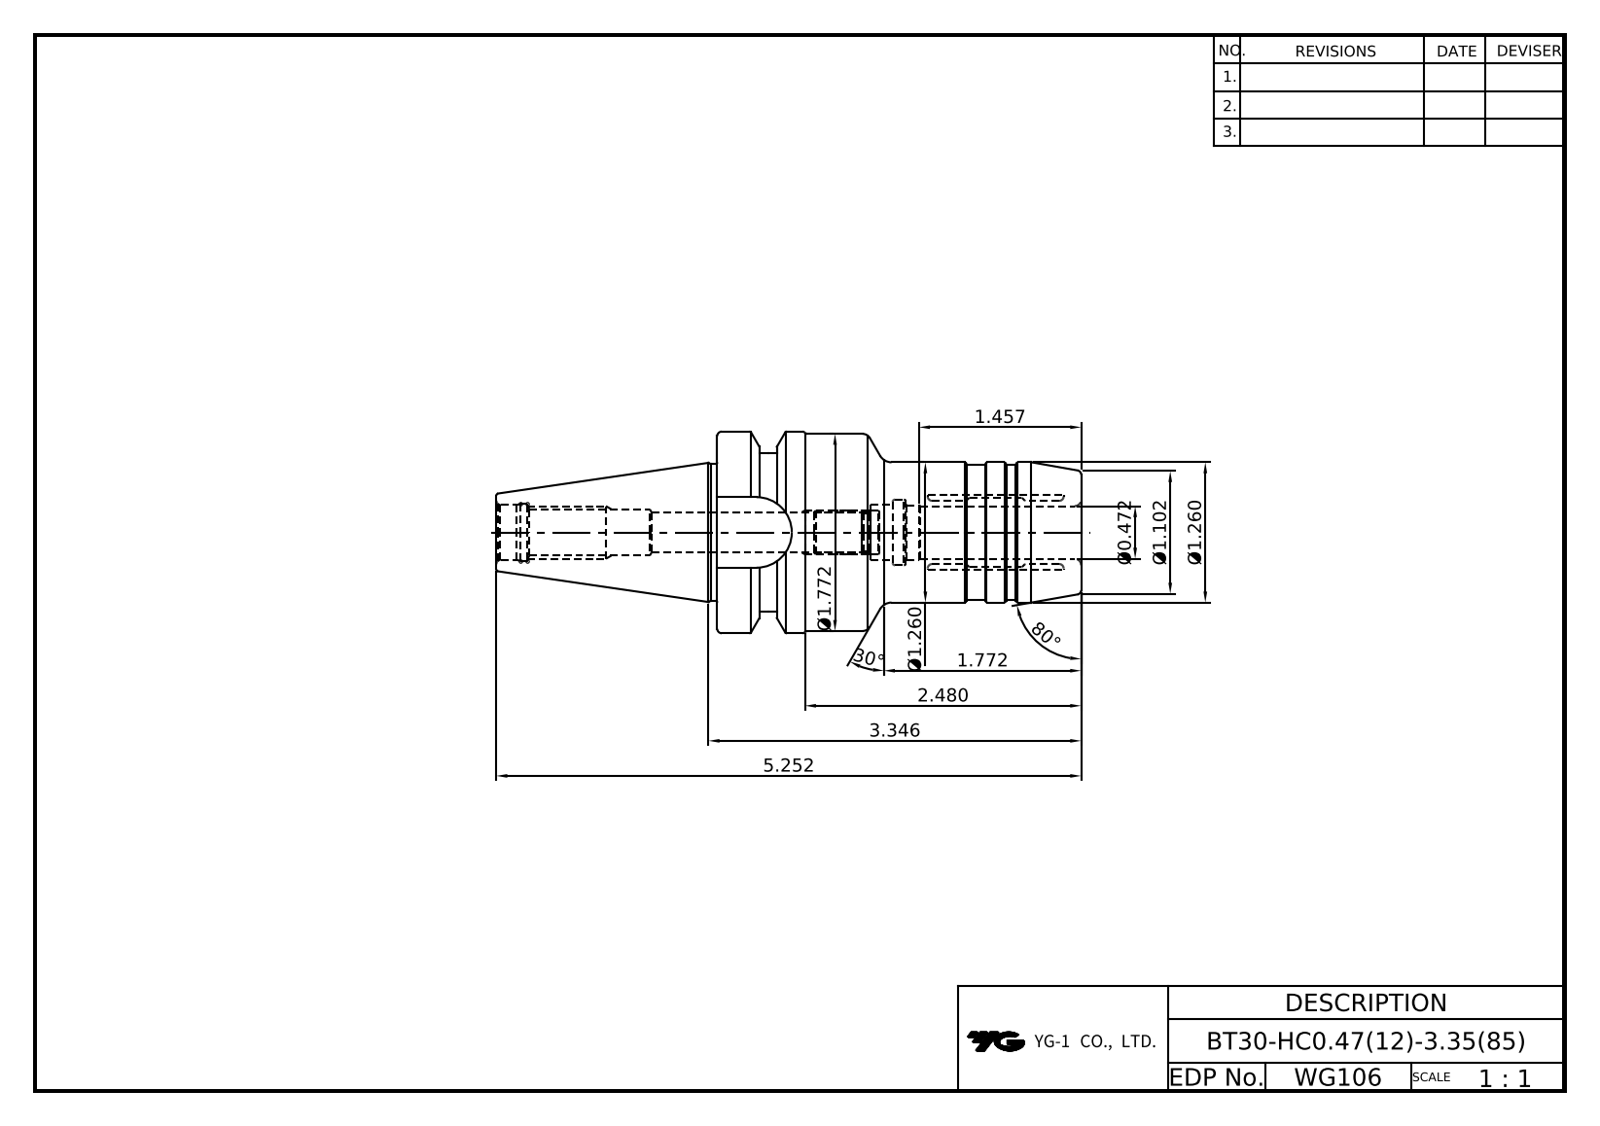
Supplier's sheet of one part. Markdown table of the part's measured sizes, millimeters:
| quantity | value |
| --- | --- |
| part name | LO-BT30ADB-HC12-85 |
| STEP written by | Autodesk Inventor 2022 (AUTOMOTIVE_DESIGN) |
| units | millimeters |
| bodies | 1 solid, 93 faces (20 planar, 38 cylindrical, 35 other) |
| overall size | 133.4 × 46 × 46 |
| volume | 101 829 mm³ |
| surface area | 21 432 mm² |
| round holes (diameter × count) | 3.24 × 4, 4 × 4, 8.92 × 1, 10.11 × 1, 12 × 1, 12.5 × 1, 12.6 × 1, 13.1 × 1 |
| round bosses / shafts (diameter × count) | 46 × 1, 44.5 × 1, 32 × 1, 31.2 × 1, 31 × 1 |
| partial cylindrical surfaces (radius × count) | 8.05 × 1, 18 × 1 |
| main face-to-face distances | 83, 32.6, 13.6, 69.4, 9.6, 4, 73.4, 16.1, 50.4, 60 |
